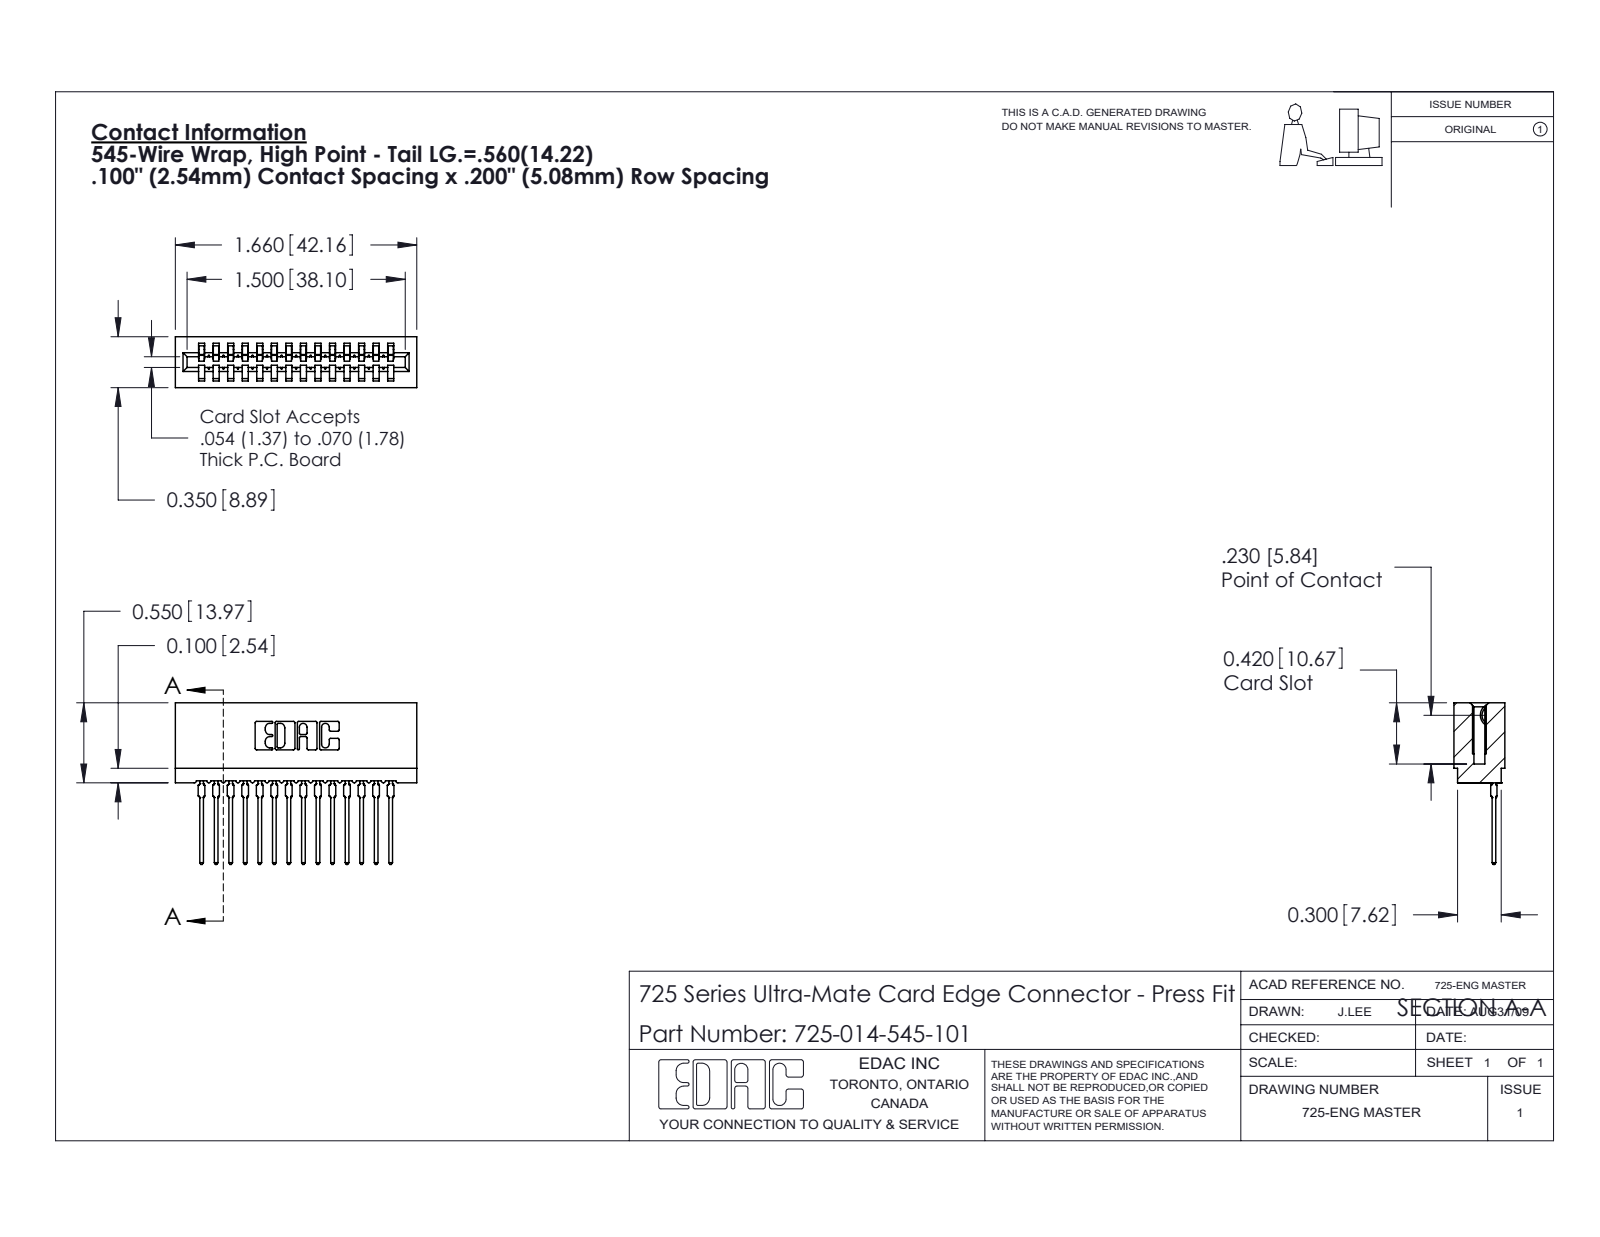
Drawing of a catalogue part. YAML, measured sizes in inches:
part_name: "745-292-001_545; 725 Part_Insulator Option - 01; 725-014-545-101"
step_written_by: "SolidWorks 2020 (CONFIG_CONTROL_DESIGN)"
units: inches
bodies: {solids: 15, faces: 1663, planar: 993, cylindrical: 306, other: 364}
overall_size: [1.66, 1.111, 0.35]
volume: 0.207
surface_area: 9.666
partial_cylinders:
  - {radius: 0.015, count: 28}
  - {radius: 0.021, count: 28}
  - {radius: 0.01, count: 22}
  - {radius: 0.007, count: 6}
  - {radius: 0.031, count: 6}
  - {radius: 0.005, count: 4}
  - {radius: 0.011, count: 4}
  - {radius: 0.026, count: 3}
face_to_face_distances: [0.1, 0.2, 0.3, 0.4, 0.5, 0.35, 0.6, 0.212, 0.138, 0.063]
